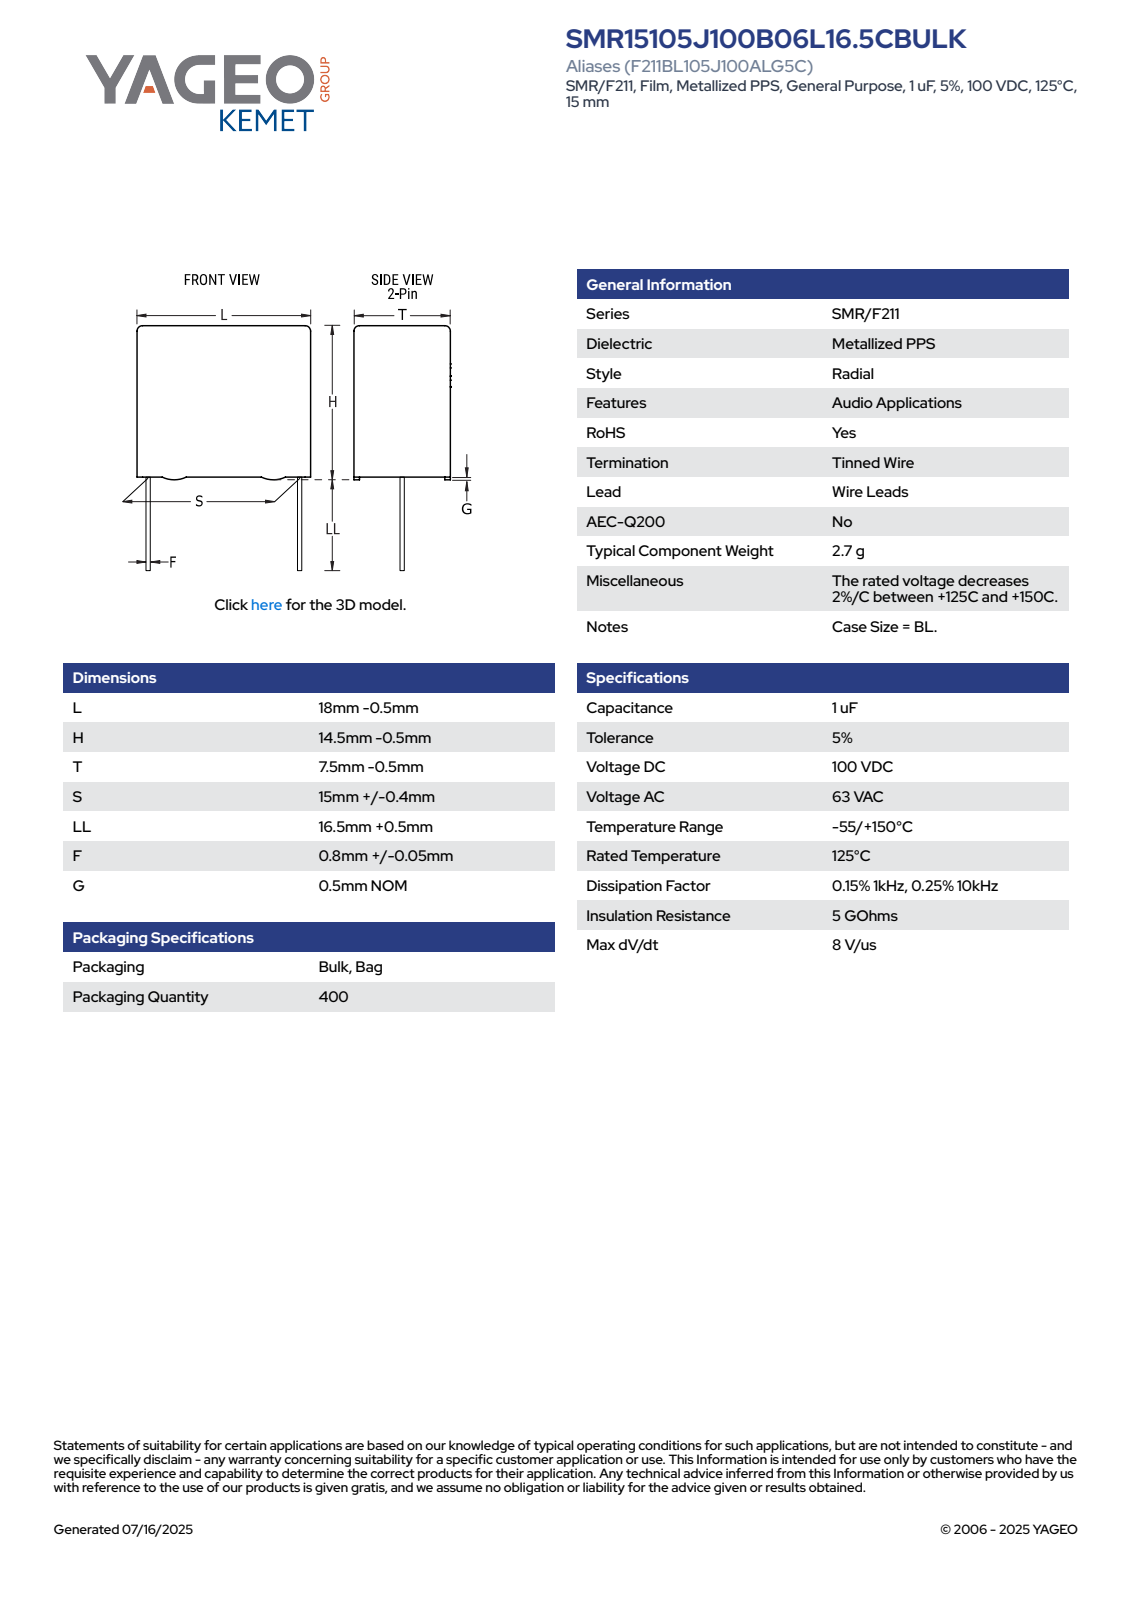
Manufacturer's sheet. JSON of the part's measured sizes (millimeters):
{"part_name": "CFR_RBG_18X14.5X7.5_L17.5H14T7S15LL17F0.85G0.5", "step_written_by": "SolidWorks 2021 (AUTOMOTIVE_DESIGN)", "units": "millimeters", "bodies": {"solids": 4, "faces": 89, "planar": 81, "cylindrical": 8, "other": 0}, "overall_size": [31, 17.5, 7], "volume_mm3": 1673, "surface_area_mm2": 1035, "round_bosses_or_shafts": [[0.85, 2]], "partial_cylinders_radius": [[0.5, 4]], "face_to_face_distances": [7, 13.5, 17.5, 0.4, 6.6, 0.5, 14, 6.2, 17, 31]}
